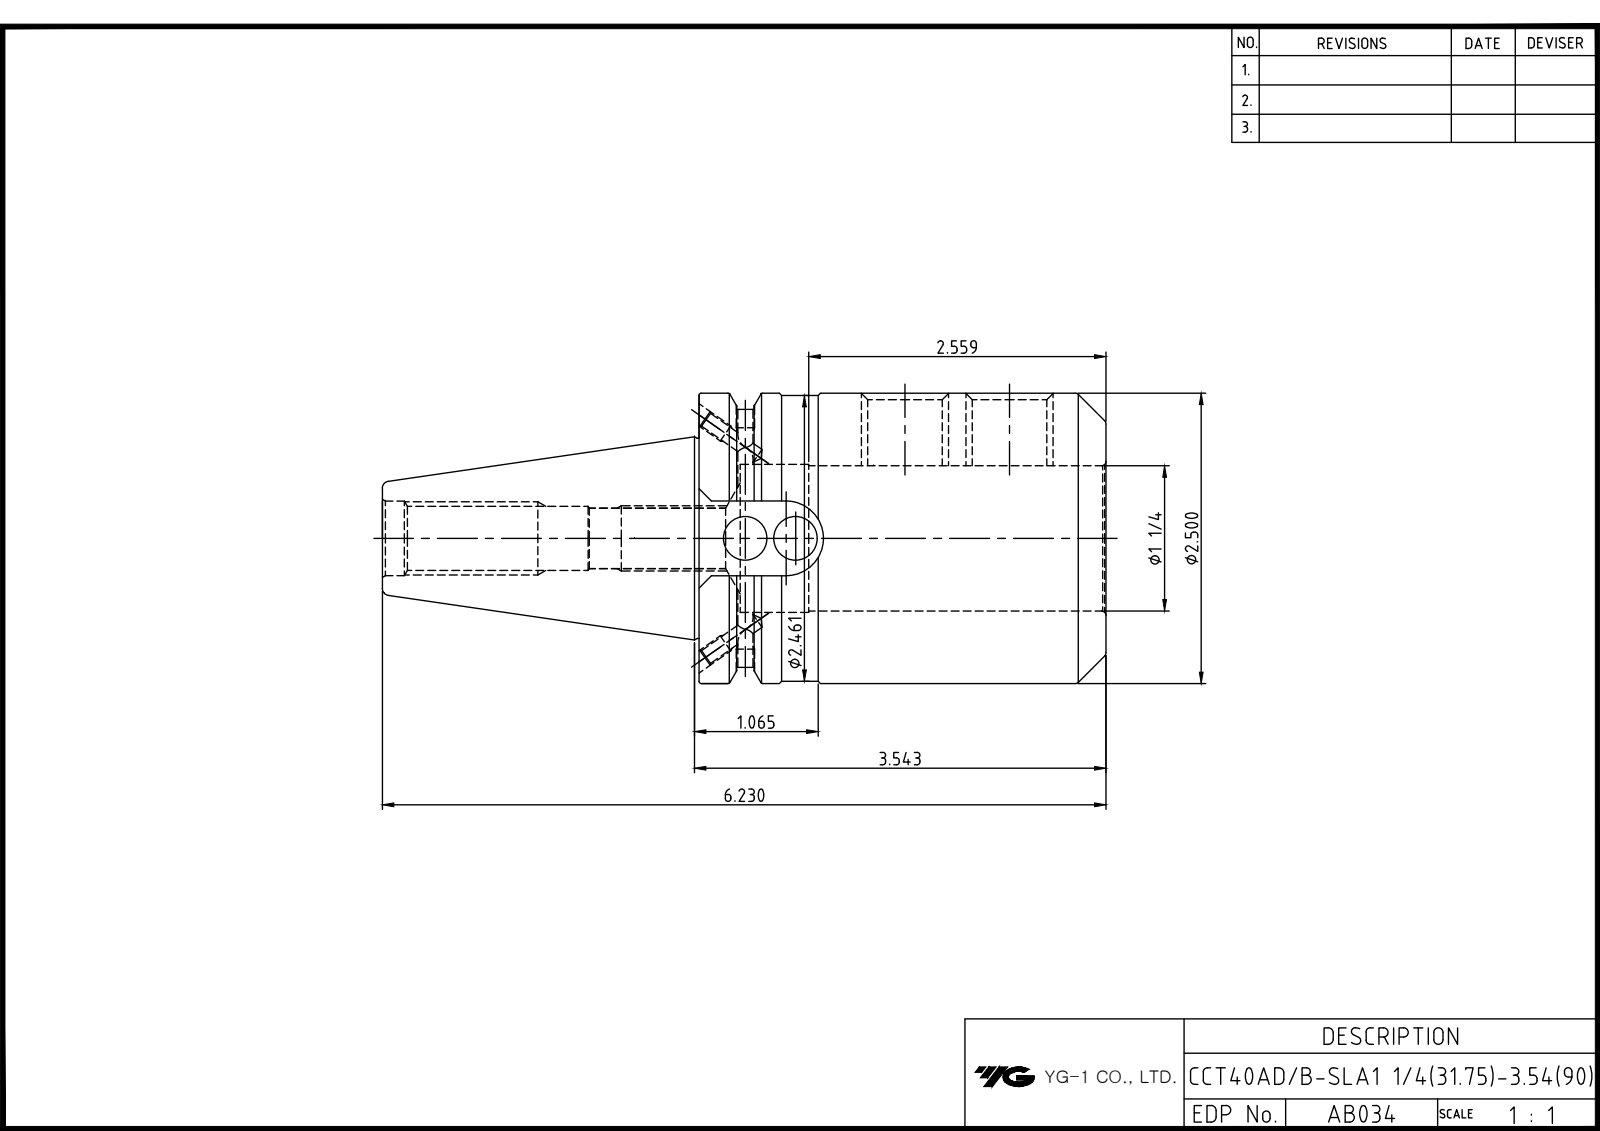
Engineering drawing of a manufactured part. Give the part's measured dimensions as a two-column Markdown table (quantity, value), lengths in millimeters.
| quantity | value |
| --- | --- |
| part name | LO-CCT40ADB-SLA31.75-90 |
| STEP written by | Autodesk Inventor 2025 (AUTOMOTIVE_DESIGN) |
| units | millimeters |
| bodies | 1 solid, 94 faces (36 planar, 33 cylindrical, 25 other) |
| overall size | 158.25 × 63.5 × 63.5 |
| volume | 250 983 mm³ |
| surface area | 43 445 mm² |
| round holes (diameter × count) | 3.24 × 4, 4 × 2, 4.2 × 2, 17.32 × 2, 9.53 × 1, 12.57 × 1, 13.39 × 1, 16.3 × 1, 31.75 × 1, 32.95 × 1 |
| round bosses / shafts (diameter × count) | 63.5 × 1, 62.5 × 1, 43.8 × 1 |
| partial cylindrical surfaces (radius × count) | 8.19 × 1, 28.15 × 1 |
| main face-to-face distances | 89, 9, 80, 47.6, 16.38, 69.25, 78.25, 158.25, 81.29, 12.04 |
| hole center spacings | 22.86 |
